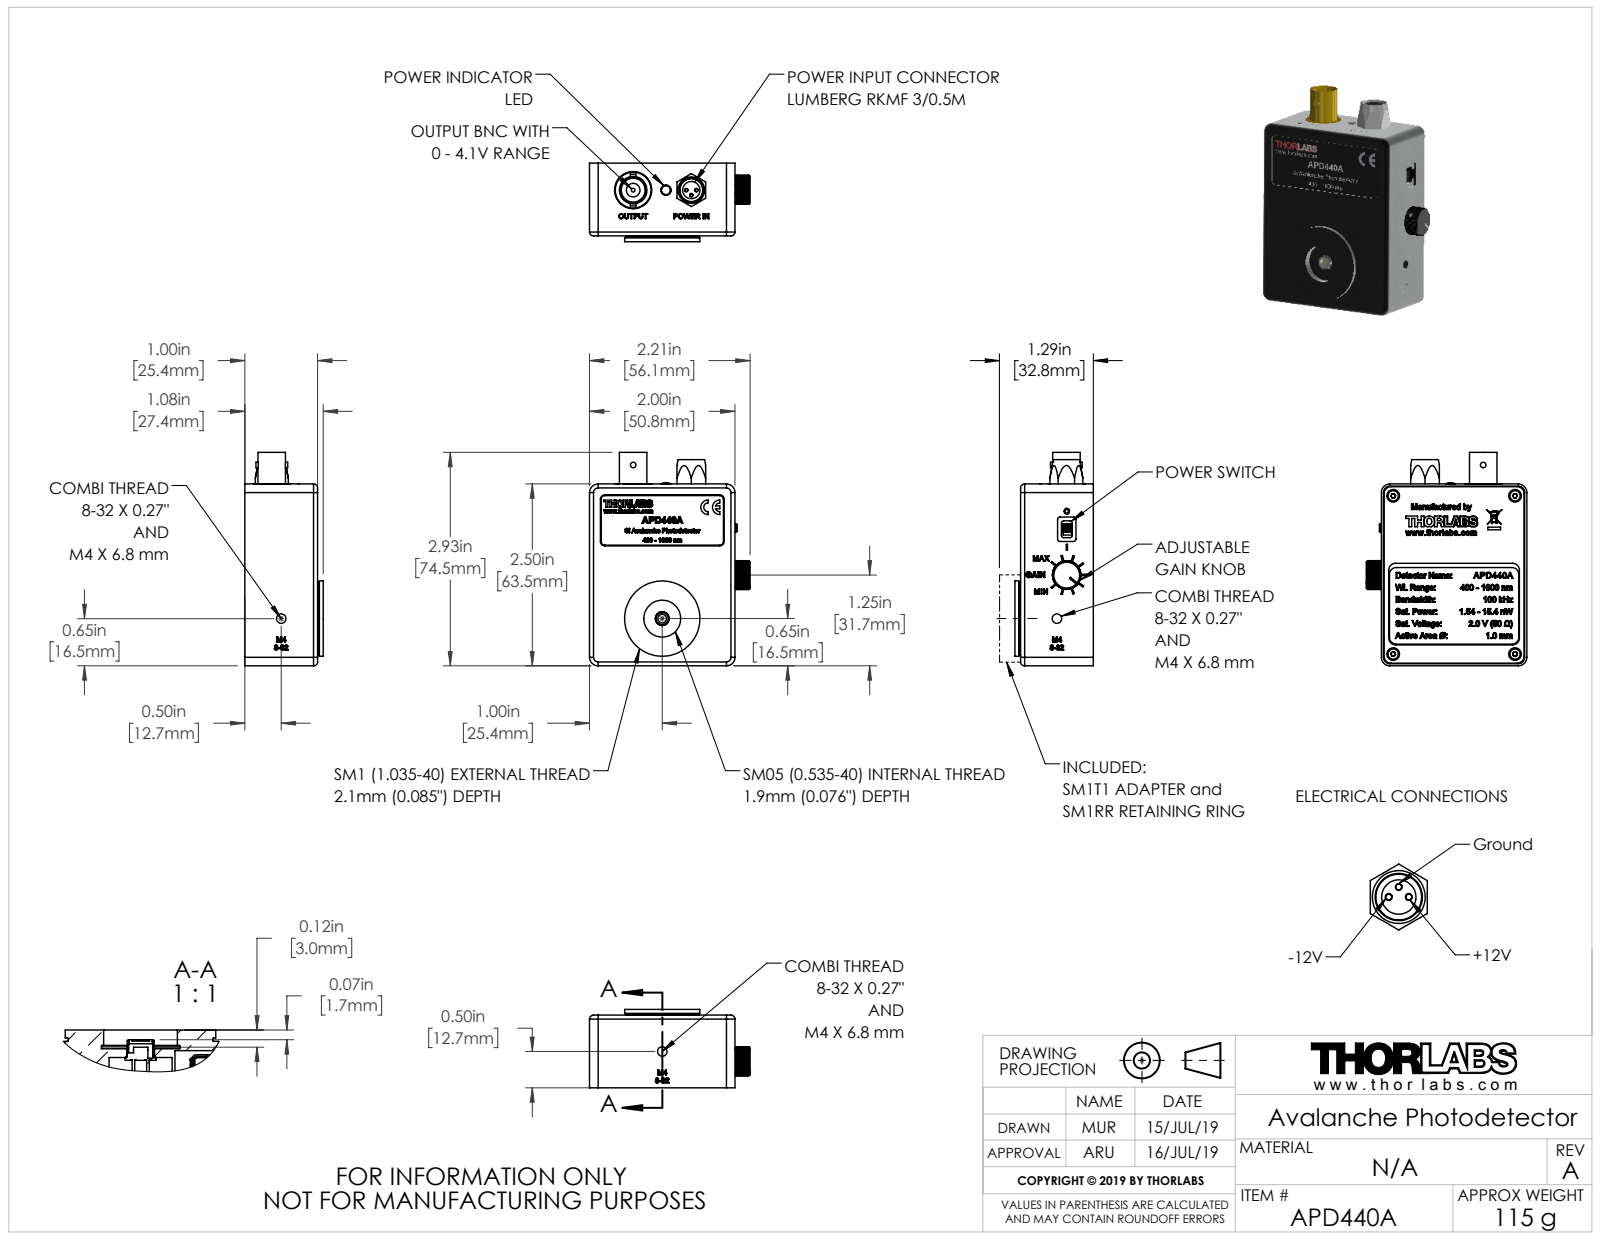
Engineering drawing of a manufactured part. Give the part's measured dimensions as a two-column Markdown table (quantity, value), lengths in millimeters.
| quantity | value |
| --- | --- |
| part name | 19.07.02_APD440-Web_Drawing |
| STEP written by | SolidWorks 2018 (CONFIG_CONTROL_DESIGN) |
| units | millimeters |
| bodies | 22 solids, 5078 faces (2838 planar, 492 cylindrical, 1748 other) |
| overall size | 74.54 × 56.08 × 27.4 |
| volume | 32 263 mm³ |
| surface area | 30 511 mm² |
| round holes (diameter × count) | 1.6 × 9, 1 × 5, 2.4 × 4, 3.3 × 2, 0.39 × 1, 0.9 × 1, 1.27 × 1, 2.2 × 1, 2.5 × 1, 2.92 × 1, 3 × 1, 3.6 × 1 |
| round bosses / shafts (diameter × count) | 2 × 9, 3.8 × 4, 1.57 × 4, 4 × 2, 0.45 × 2, 26.29 × 1, 25.3 × 1, 12.6 × 1 |
| partial cylindrical surfaces (radius × count) | 0.3 × 50, 0.15 × 24, 0.4 × 24, 2.5 × 21, 1 × 12, 3.3 × 10, 0.8 × 8, 2.4 × 8 |
| main face-to-face distances | 1.58, 2.5, 1.6, 23.8, 23.78, 22.2, 25.38, 48.3, 24.87, 23.29 |
| hole center spacings | 4.39, 51.14, 24.61, 24.62, 41.23, 41.24, 42.55, 47.86 |
